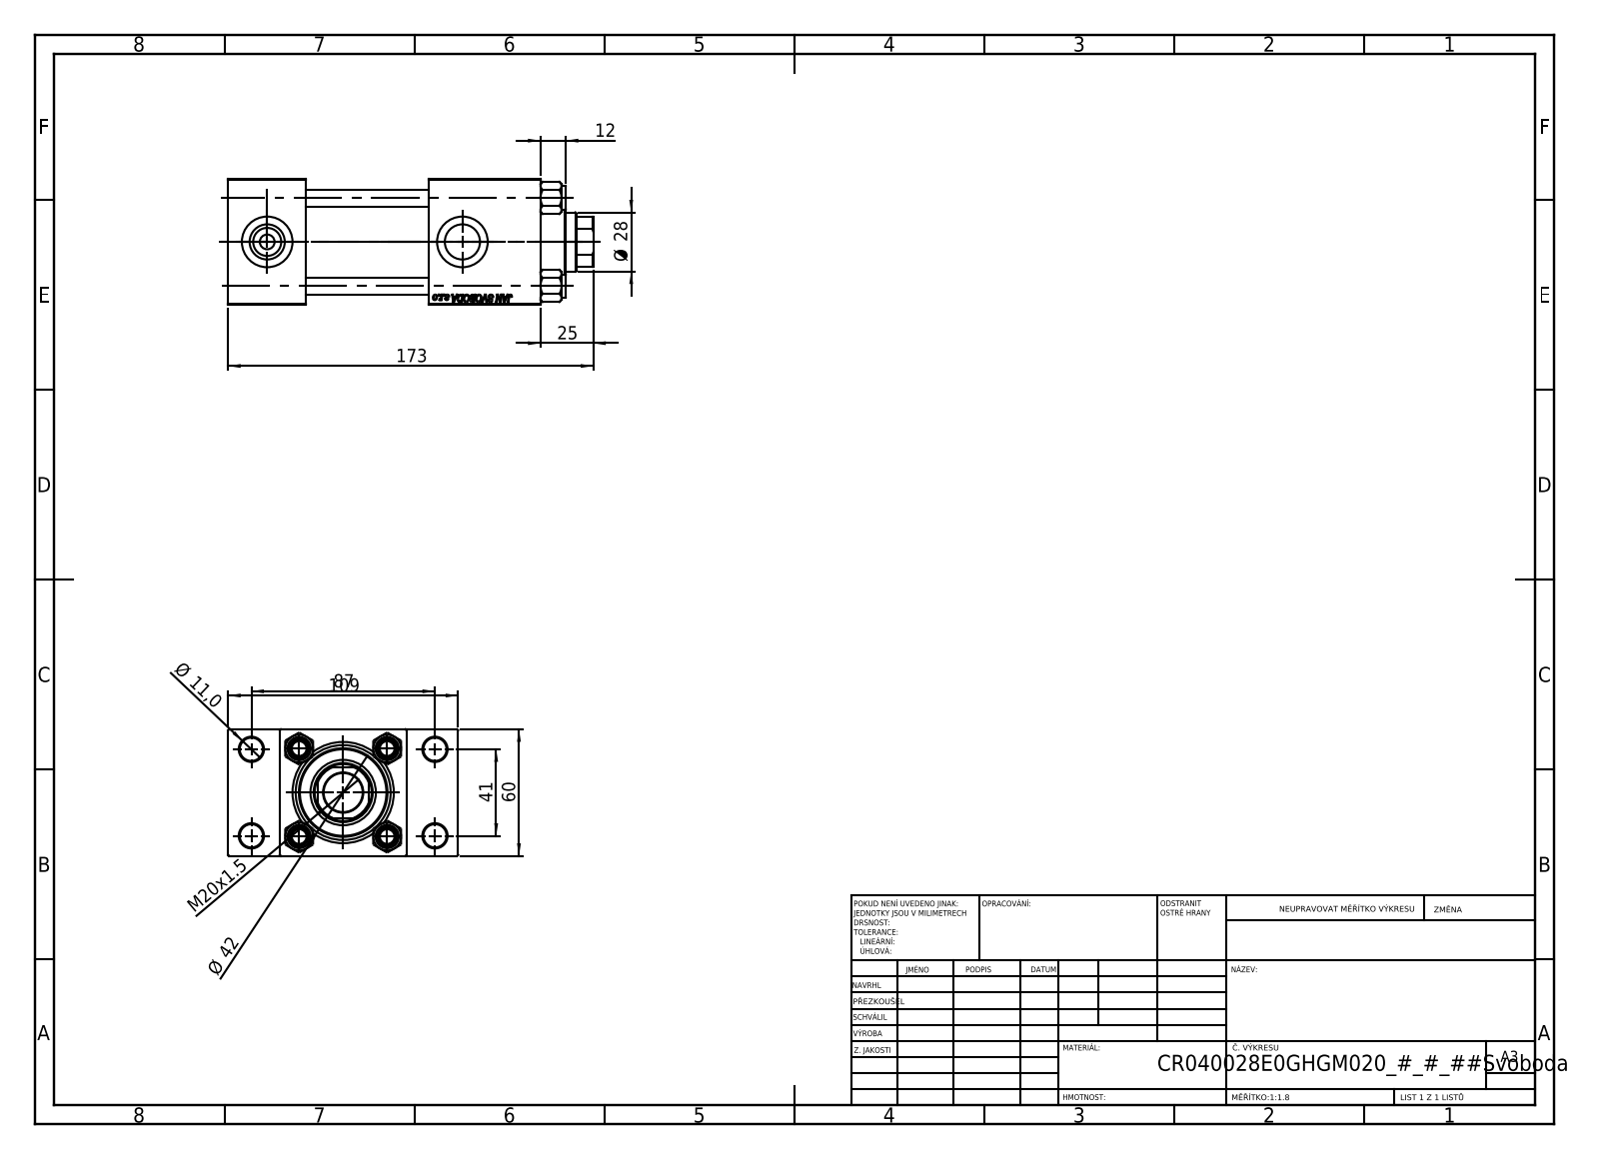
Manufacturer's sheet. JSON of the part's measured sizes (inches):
{"part_name": "V215CR_TYCINKA_E; V215CR_VCP_E; NUT_M5_E; V215_VC_A (+1 more)", "step_written_by": "SolidWorks 2019 (CONFIG_CONTROL_DESIGN)", "units": "inches", "bodies": {"solids": 11, "faces": 1136, "planar": 498, "cylindrical": 86, "other": 552}, "overall_size": [6.811, 4.291, 2.362], "volume_in3": 31.85, "surface_area_in2": 203, "round_holes": [[0.315, 4], [0.433, 4], [0.276, 2], [0.656, 2], [0.945, 2], [0.728, 1], [1.102, 1], [1.22, 1], [1.575, 1], [1.772, 1]], "round_bosses_or_shafts": [[0.433, 4], [1.811, 1], [1.654, 1]], "partial_cylinders_radius": [[0.531, 1]], "face_to_face_distances": [2.362, 1.457, 0.965, 3.327, 2.283, 3.74, 2.087, 0.957, 5.827, 4.37], "hole_center_spacings": [0.892, 1.161, 1.642, 1.856, 1.893, 2.533, 3.011, 1.614]}
